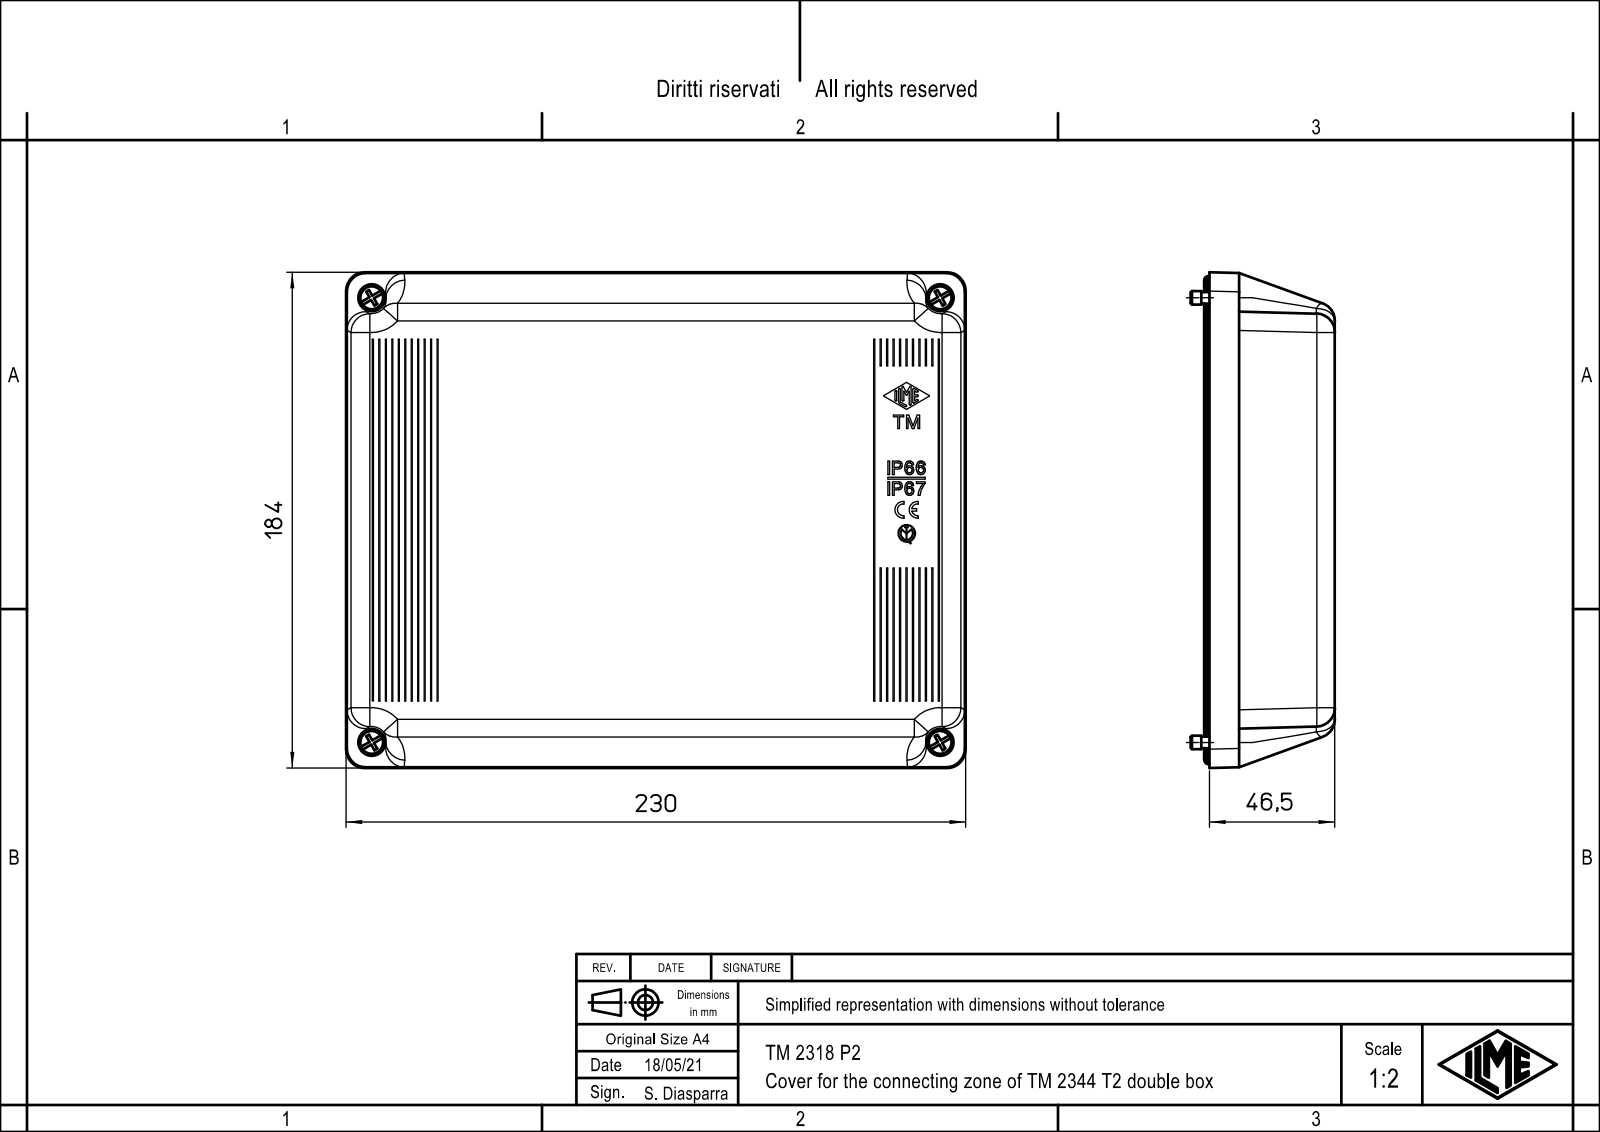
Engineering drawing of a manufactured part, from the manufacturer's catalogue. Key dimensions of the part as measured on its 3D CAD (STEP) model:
Part name (STEP PRODUCT): 39050_coperchioTM2318P2
STEP written by: Creo Elements/Direct Modeling 20.1B 02-Apr-2019 (C) Parametric Technology GmbH (AUTOMOTIVE_DESIGN)
Units: millimetres
Bodies: 1 solid, 1083 faces (882 planar, 133 cylindrical, 68 other)
Overall size (bounding box): 230 × 184 × 53.9
Volume: 433 071 mm³ · Surface area: 147 093 mm²
Round holes (diameter × count): ⌀5.94 ×1
Round bosses / shafts (diameter × count): ⌀8.5 ×4, ⌀5 ×4, ⌀4.3 ×4, ⌀6.56 ×1
Partial cylindrical surfaces — rounded edges, fillets, slot ends (radius × count): R1.5 ×16, R7 ×14, R2 ×12, R6 ×12, R0.33 ×11, R3 ×4, R10 ×4, R11.5 ×4
Main face-to-face distances: 5, 5.14, 7, 41.5, 46.5, 22.3, 7.01, 4.8, 6.99, 46.3
